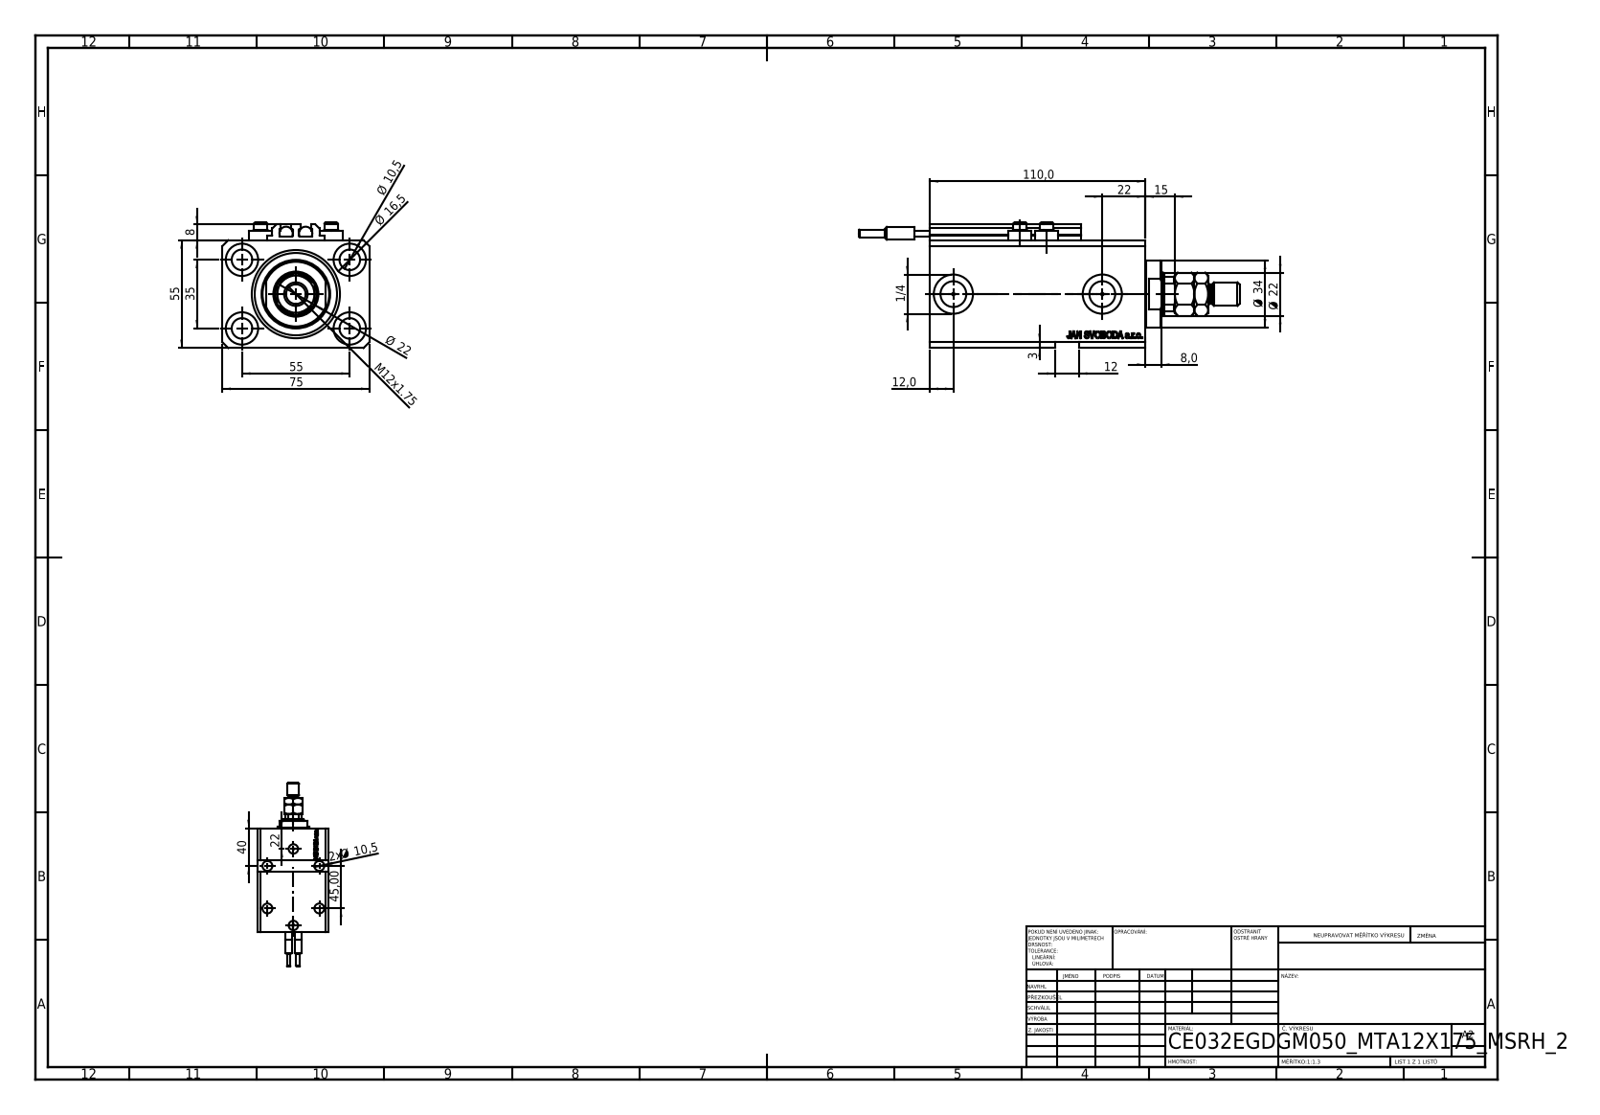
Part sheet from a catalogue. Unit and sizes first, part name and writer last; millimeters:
Units: millimetres
Overall size (bounding box): 194 × 75 × 64
Round holes (diameter × count): ⌀10.5 ×9, ⌀1.25 ×4, ⌀4 ×4, ⌀16.5 ×4, ⌀10 ×2, ⌀13.16 ×2, ⌀20 ×2, ⌀22 ×1, ⌀32 ×1, ⌀45 ×1
Round bosses / shafts (diameter × count): ⌀11.6 ×4, ⌀7 ×4, ⌀6.8 ×2, ⌀6.5 ×2, ⌀4 ×2, ⌀34 ×1, ⌀12 ×1, ⌀10 ×1
Partial cylindrical surfaces — rounded edges, fillets, slot ends (radius × count): R0.2 ×10, R10.5 ×1
Main face-to-face distances: 55, 75, 15, 3, 110, 57, 95, 9.9, 85.1, 100.1
Hole centre spacings: 32.6, 32.87, 55, 68.74, 13.6, 14.09, 23.05, 25.81
Volume: 388 266 mm³ · Surface area: 101 858 mm²
Bodies: 11 solids, 1201 faces (565 planar, 174 cylindrical, 462 other)
Part name (STEP PRODUCT): MTA; V250CE_C_VCP; ALLEN BOLT V250CE; V250CE_VC_E (+2 more)
STEP written by: SolidWorks 2019 (CONFIG_CONTROL_DESIGN)
